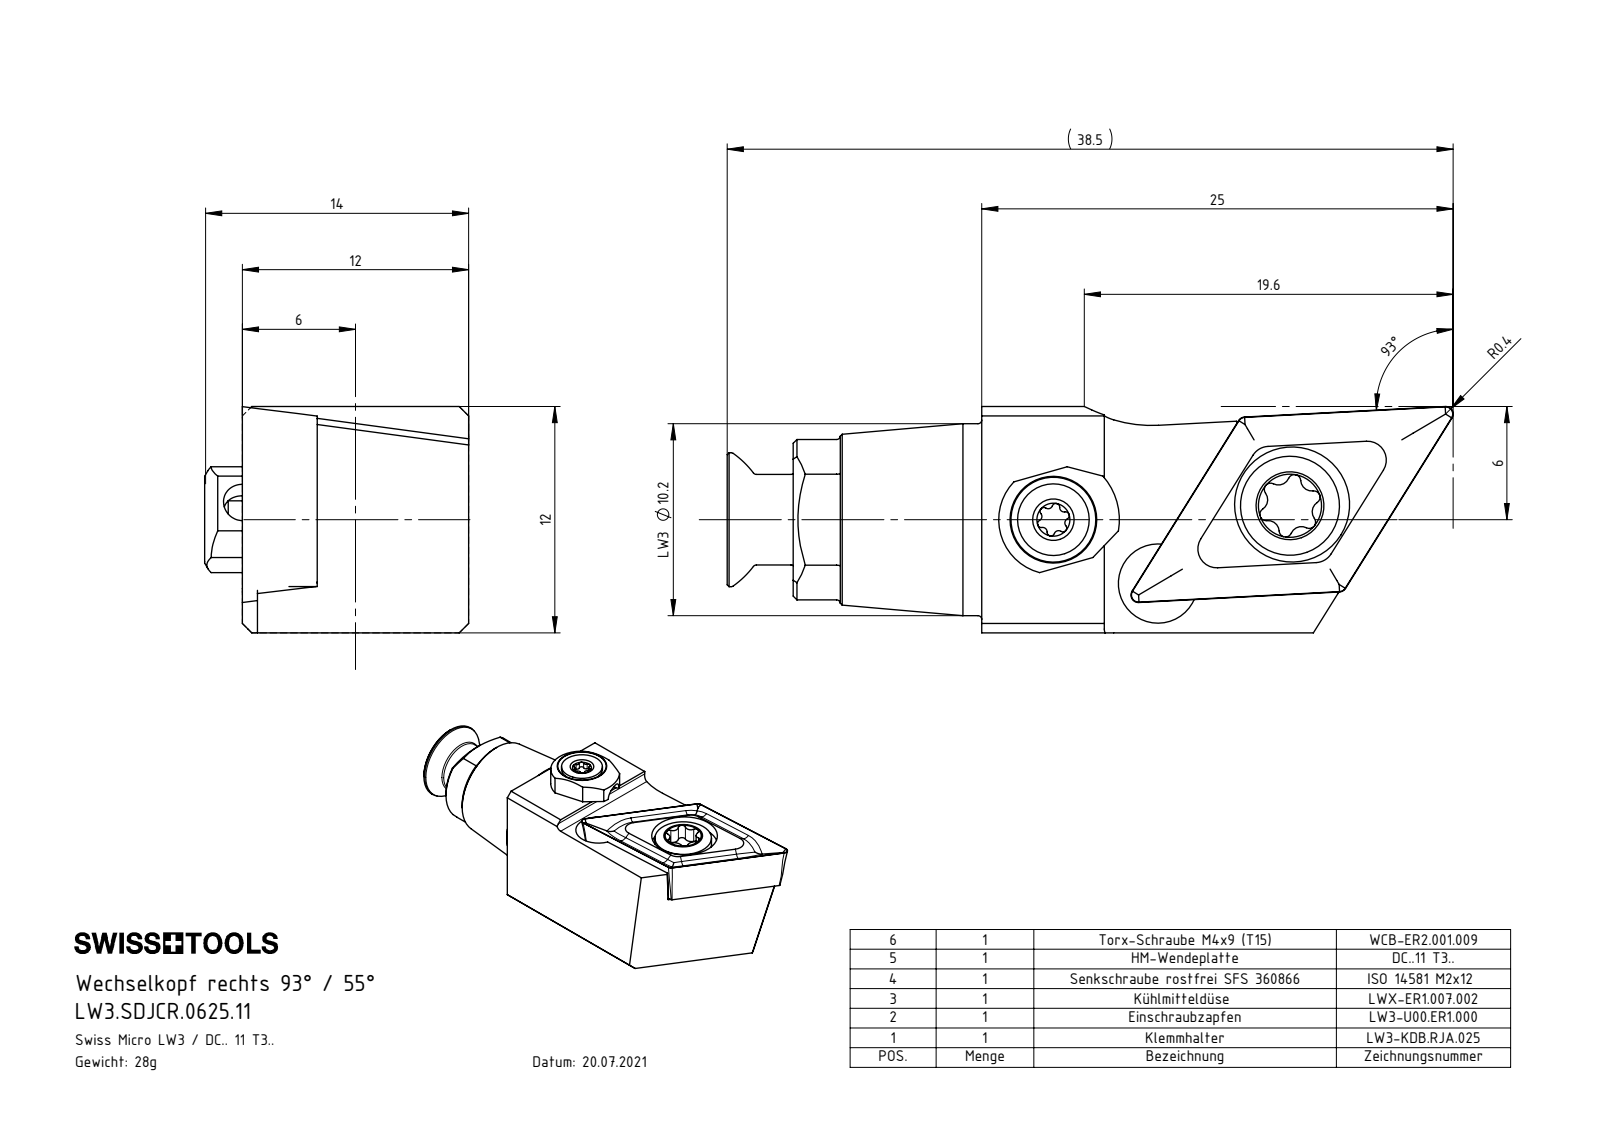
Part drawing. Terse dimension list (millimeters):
name: LWX-ER1.007.002; ISO 14581 - M2x12; LW3.KDB.RJA.025; DCMT11T304 (+3 more)
written by: SolidWorks 2017 (AUTOMOTIVE_DESIGN)
unit: mm
bodies: 6 solids, 189 faces (69 planar, 52 cylindrical, 68 other)
size: 38.51 × 14 × 12
volume: 3 273 mm³; area: 2 868 mm²
holes: 1× ⌀1.6, 1× ⌀2, 1× ⌀2.5, 1× ⌀3, 1× ⌀3.3, 1× ⌀4.2, 1× ⌀4.4, 1× ⌀5.5, 1× ⌀6.1
bosses: 1× ⌀10.18, 1× ⌀6.9, 1× ⌀6, 1× ⌀5.25, 1× ⌀5, 1× ⌀4.8, 1× ⌀4, 1× ⌀3.8
rounds: 8× R0.2, 6× R0.24, 6× R0.34, 6× R0.59, 1× R0.5, 1× R1, 1× R2.9, 1× R3.5
face distances: 12, 8.03, 3.97, 11.2, 3.17, 0.8, 2, 2.5, 13.5, 11.5
hole spacings: 6.5, 8.13, 8.25, 12.57, 12.69
